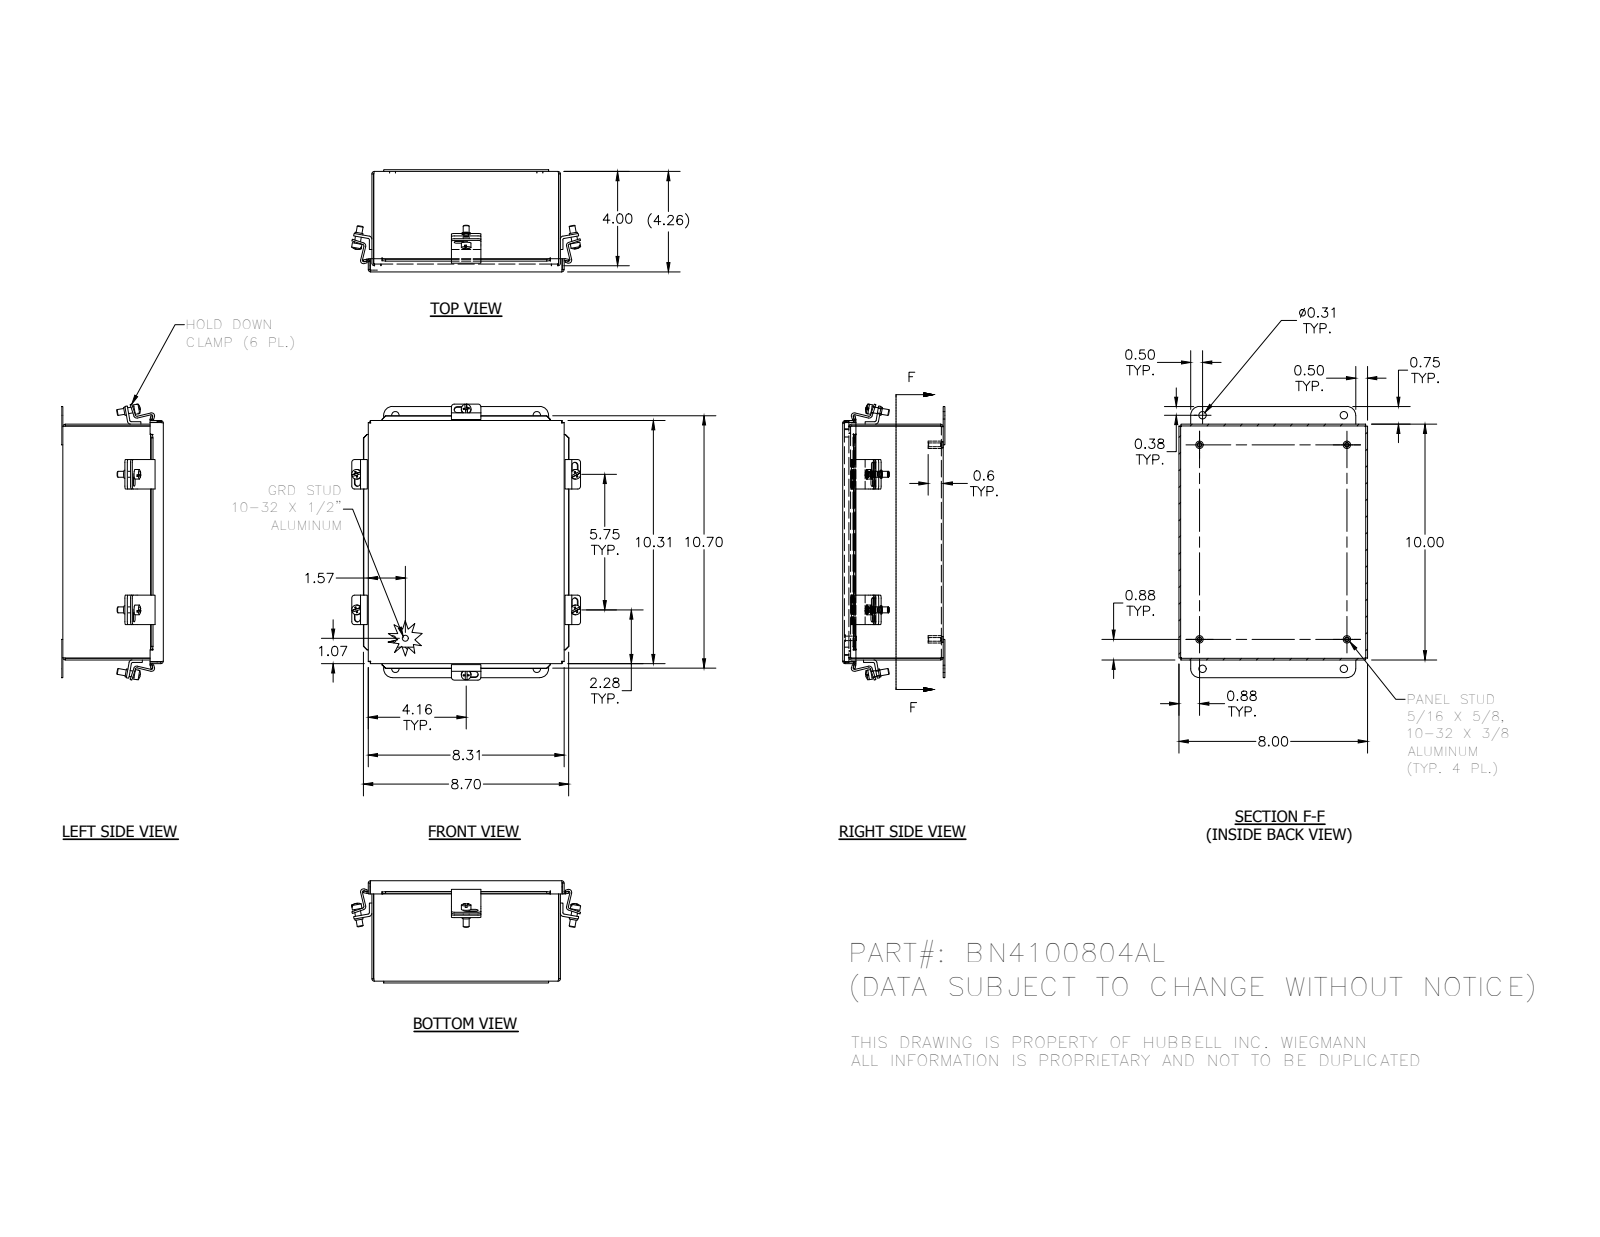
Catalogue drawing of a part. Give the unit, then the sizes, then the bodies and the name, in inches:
Units: inches
Overall size (bounding box): 11.706 × 9.711 × 4.336
Round holes (diameter × count): ⌀0.196 ×6, ⌀0.156 ×4, ⌀0.25 ×4, ⌀0.31 ×4
Round bosses / shafts (diameter × count): ⌀0.25 ×9, ⌀0.41 ×6, ⌀0.344 ×6, ⌀0.313 ×4, ⌀0.19 ×1
Partial cylindrical surfaces — rounded edges, fillets, slot ends (radius × count): R0.125 ×24, R0.031 ×16, R0.105 ×16, R0.063 ×12, R0.126 ×12, R0.133 ×12, R0.375 ×4
Main face-to-face distances: 0.074, 4.187, 4.261, 4.113, 7.926, 9.926, 3.926, 0.261, 8, 7.852
Hole centre spacings: 6.25, 1.256, 9.501, 6.251, 11.304, 1.256, 5.75, 6
Volume: 32.74 in³ · Surface area: 839.2 in²
Bodies: 29 solids, 657 faces (363 planar, 224 cylindrical, 70 other)
Part name (STEP PRODUCT): C2002_1; 3887_1; BN4100804ALBKP_1; BN4100804AL (+6 more)
STEP written by: SolidWorks 2014 (AUTOMOTIVE_DESIGN)
